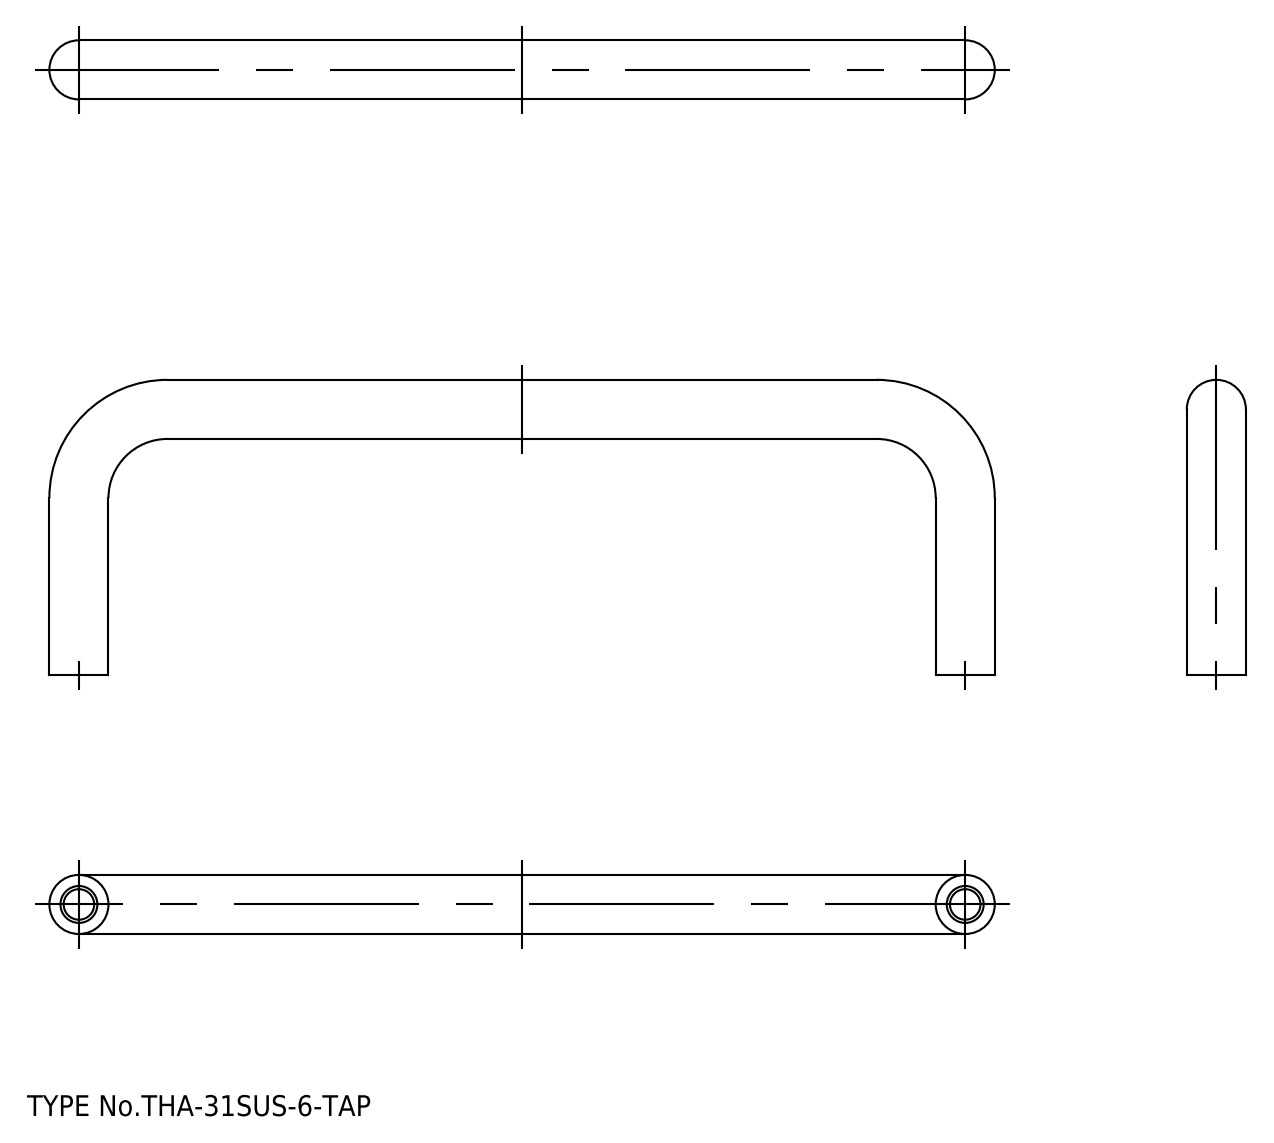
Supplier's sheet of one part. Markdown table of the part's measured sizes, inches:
| quantity | value |
| --- | --- |
| STEP written by | spGate 17.5.2 (AUTOMOTIVE_DESIGN) |
| units | inches |
| bodies | 1 solid, 18 faces (4 planar, 10 cylindrical, 4 other) |
| overall size | 5.039 × 1.575 × 0.315 |
| volume | 0.533 in³ |
| surface area | 7.721 in² |
| round holes (diameter × count) | 0.197 × 2 |
| round bosses / shafts (diameter × count) | 0.315 × 3 |
| main face-to-face distances | 0.394 |
| hole center spacings | 4.724 |
